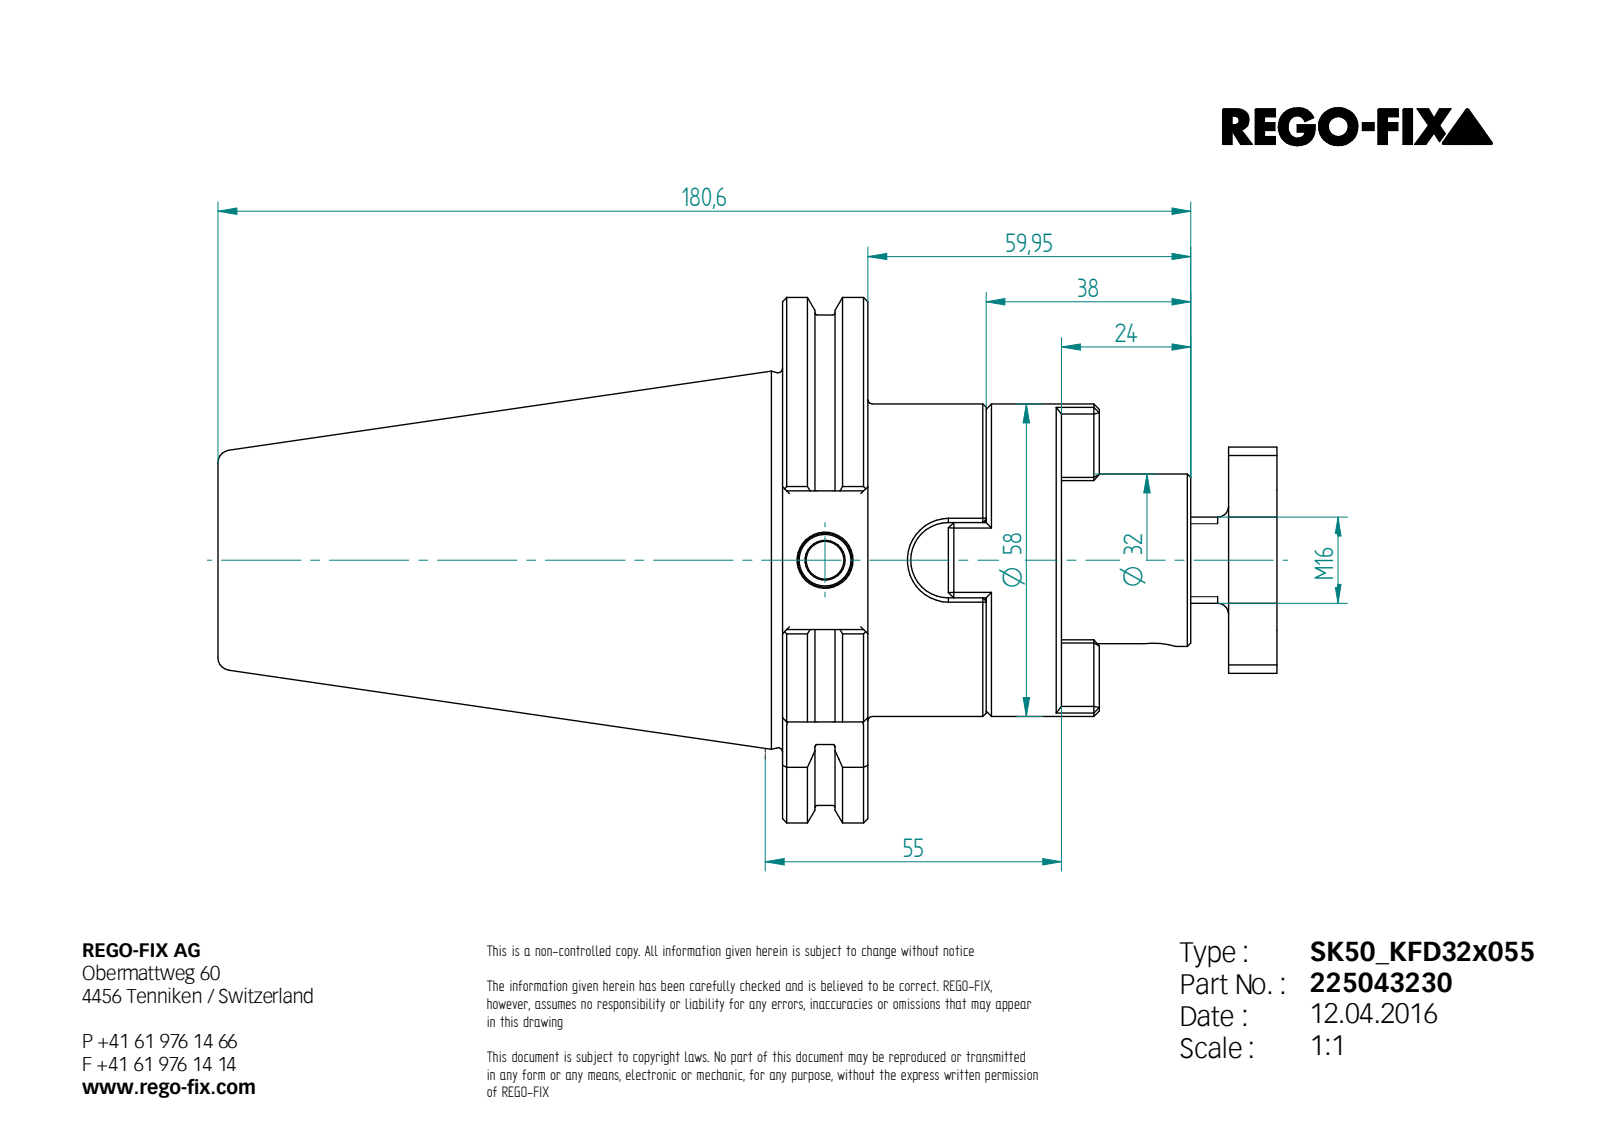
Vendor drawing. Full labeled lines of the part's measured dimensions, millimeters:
STEP written by: Unknown (AUTOMOTIVE_DESIGN)
Units: millimetres
Bodies: 3 solids, 232 faces (131 planar, 40 cylindrical, 61 other)
Overall size (bounding box): 196.6 × 97.5 × 93.58
Volume: 439 587 mm³ · Surface area: 67 740 mm²
Round holes (diameter × count): ⌀7 ×1, ⌀10 ×1, ⌀13.84 ×1, ⌀17 ×1, ⌀20.75 ×1, ⌀25 ×1, ⌀32 ×1
Round bosses / shafts (diameter × count): ⌀91 ×1, ⌀58 ×1, ⌀31.4 ×1, ⌀16 ×1
Partial cylindrical surfaces — rounded edges, fillets, slot ends (radius × count): R0.5 ×5, R5 ×4, R4 ×2, R7 ×1, R21 ×1, R48.75 ×1
Main face-to-face distances: 15.85, 37.8, 21.95, 14, 51.8, 54, 35.95, 91.8, 75.95, 40
